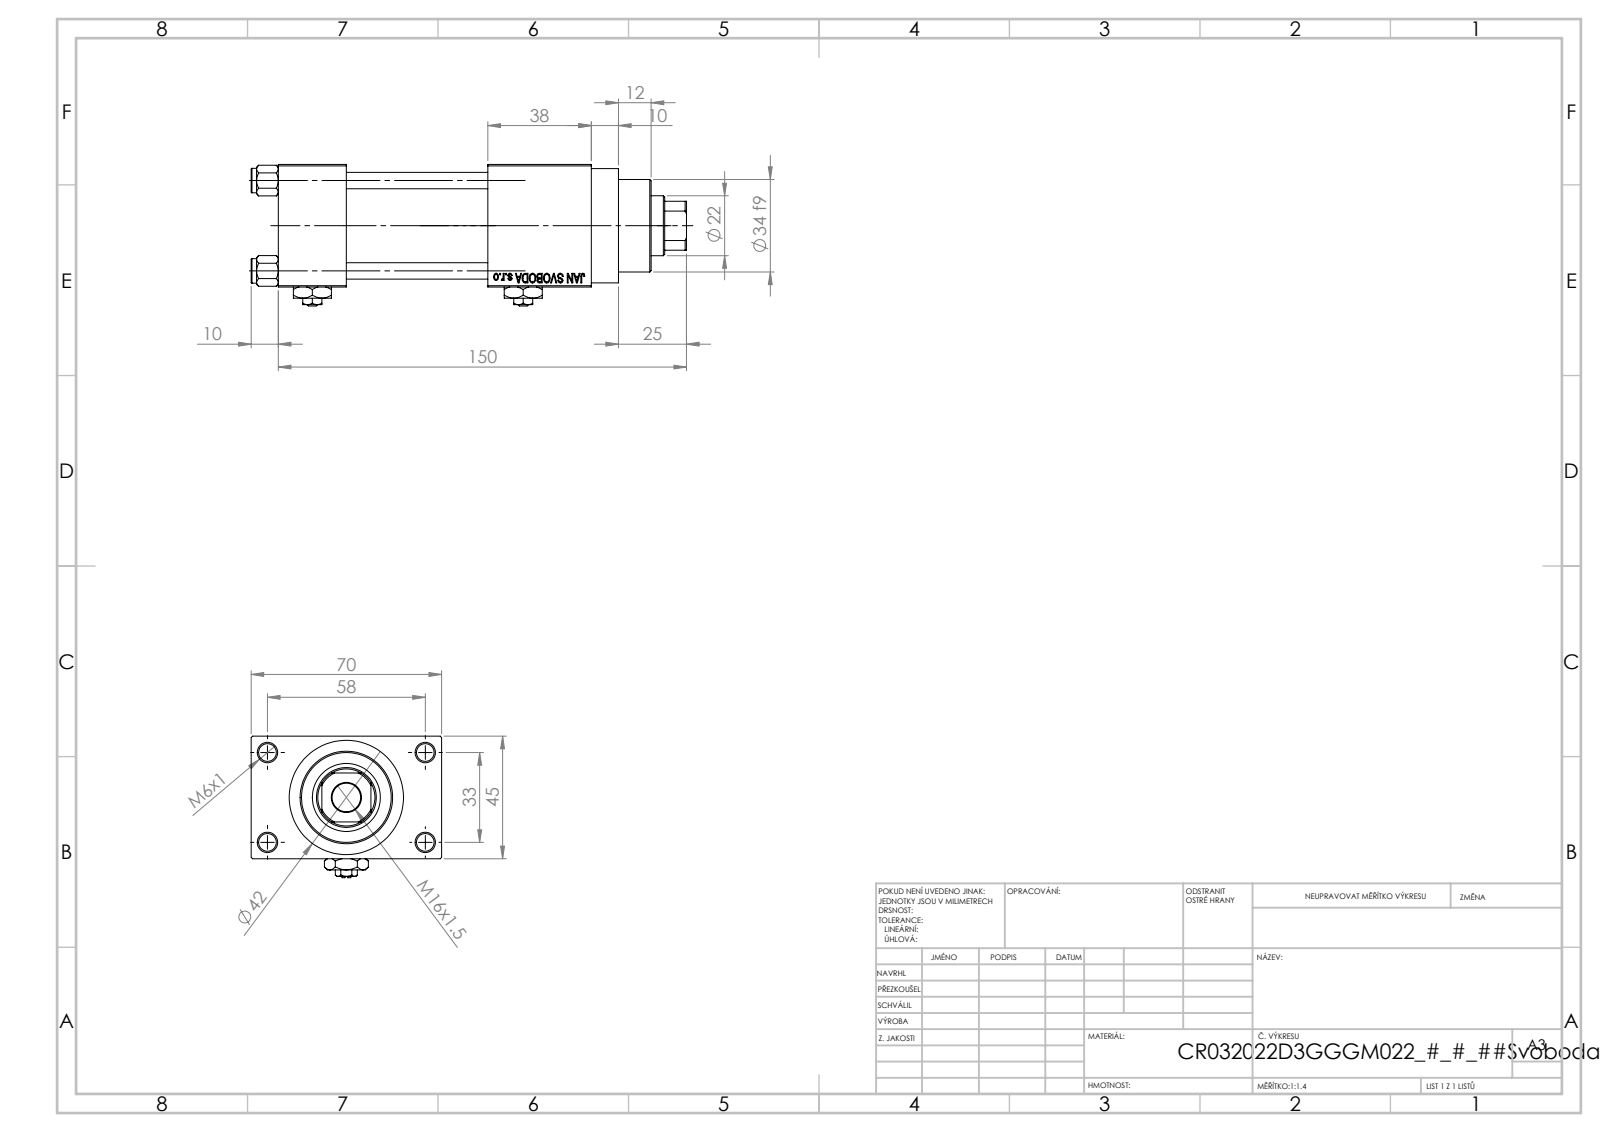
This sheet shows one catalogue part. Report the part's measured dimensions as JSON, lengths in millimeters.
{"part_name": "V215CR_D_TYCINKA; V215CR_D_Body; NUT_M5_D; V215_VC_A (+2 more)", "step_written_by": "SolidWorks 2019 (CONFIG_CONTROL_DESIGN)", "units": "millimeters", "bodies": {"solids": 13, "faces": 1202, "planar": 542, "cylindrical": 100, "other": 560}, "overall_size": [160, 70, 52], "volume_mm3": 245014, "surface_area_mm2": 81929, "round_holes": [[6, 4], [6.5, 4], [7, 2], [13.16, 2], [20, 2], [10.5, 1], [22, 1], [24, 1], [25, 1], [32, 1], [33, 1]], "round_bosses_or_shafts": [[9, 4], [42, 1], [38, 1], [34, 1]], "partial_cylinders_radius": [[10.5, 1]], "face_to_face_distances": [45, 25, 57.5, 12.5, 52, 70, 77, 90, 38, 115], "hole_center_spacings": [12.4, 23.48, 33.2, 33.37, 35.35, 45.6, 56.35, 33]}
